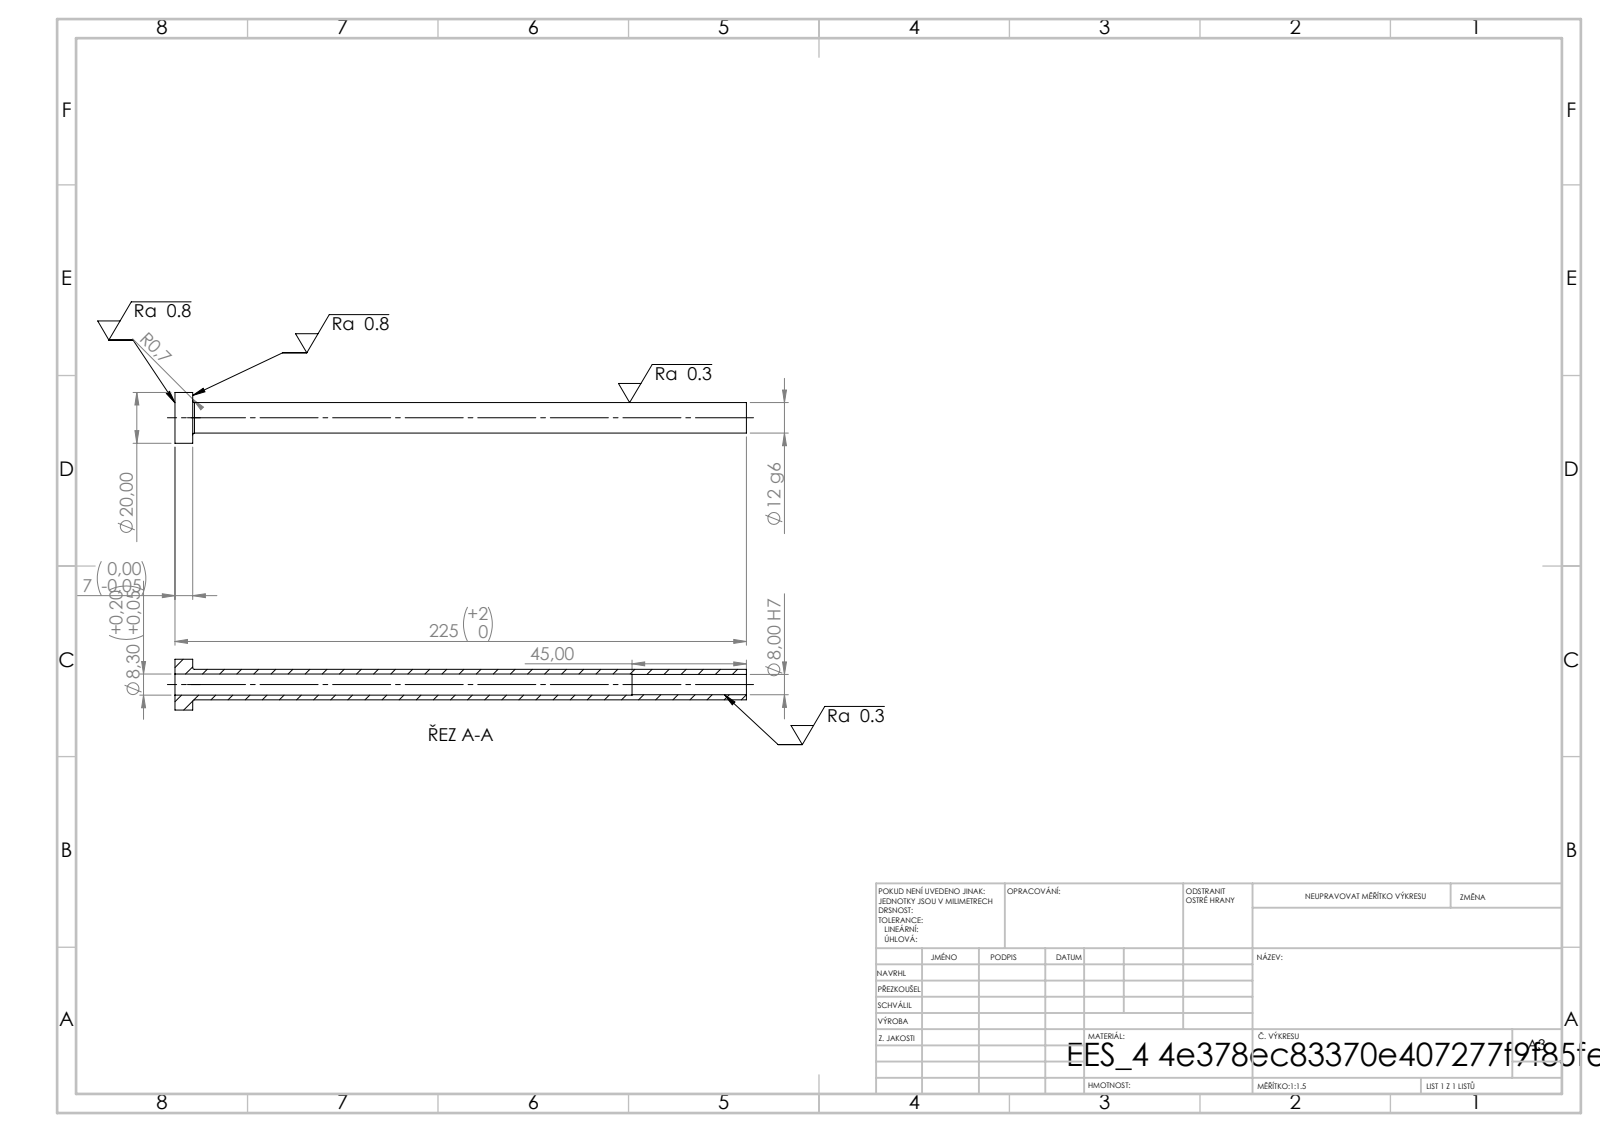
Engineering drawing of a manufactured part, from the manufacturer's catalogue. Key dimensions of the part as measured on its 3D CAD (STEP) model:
STEP written by: SolidWorks 2019 (CONFIG_CONTROL_DESIGN)
Units: millimetres
Bodies: 1 solid, 14 faces (4 planar, 8 cylindrical, 2 other)
Overall size (bounding box): 225 × 20 × 20
Volume: 14 857 mm³ · Surface area: 14 999 mm²
Round holes (diameter × count): ⌀8 ×1, ⌀8.3 ×1
Round bosses / shafts (diameter × count): ⌀20 ×1, ⌀12 ×1
Main face-to-face distances: 7, 225, 218, 180, 173, 45
